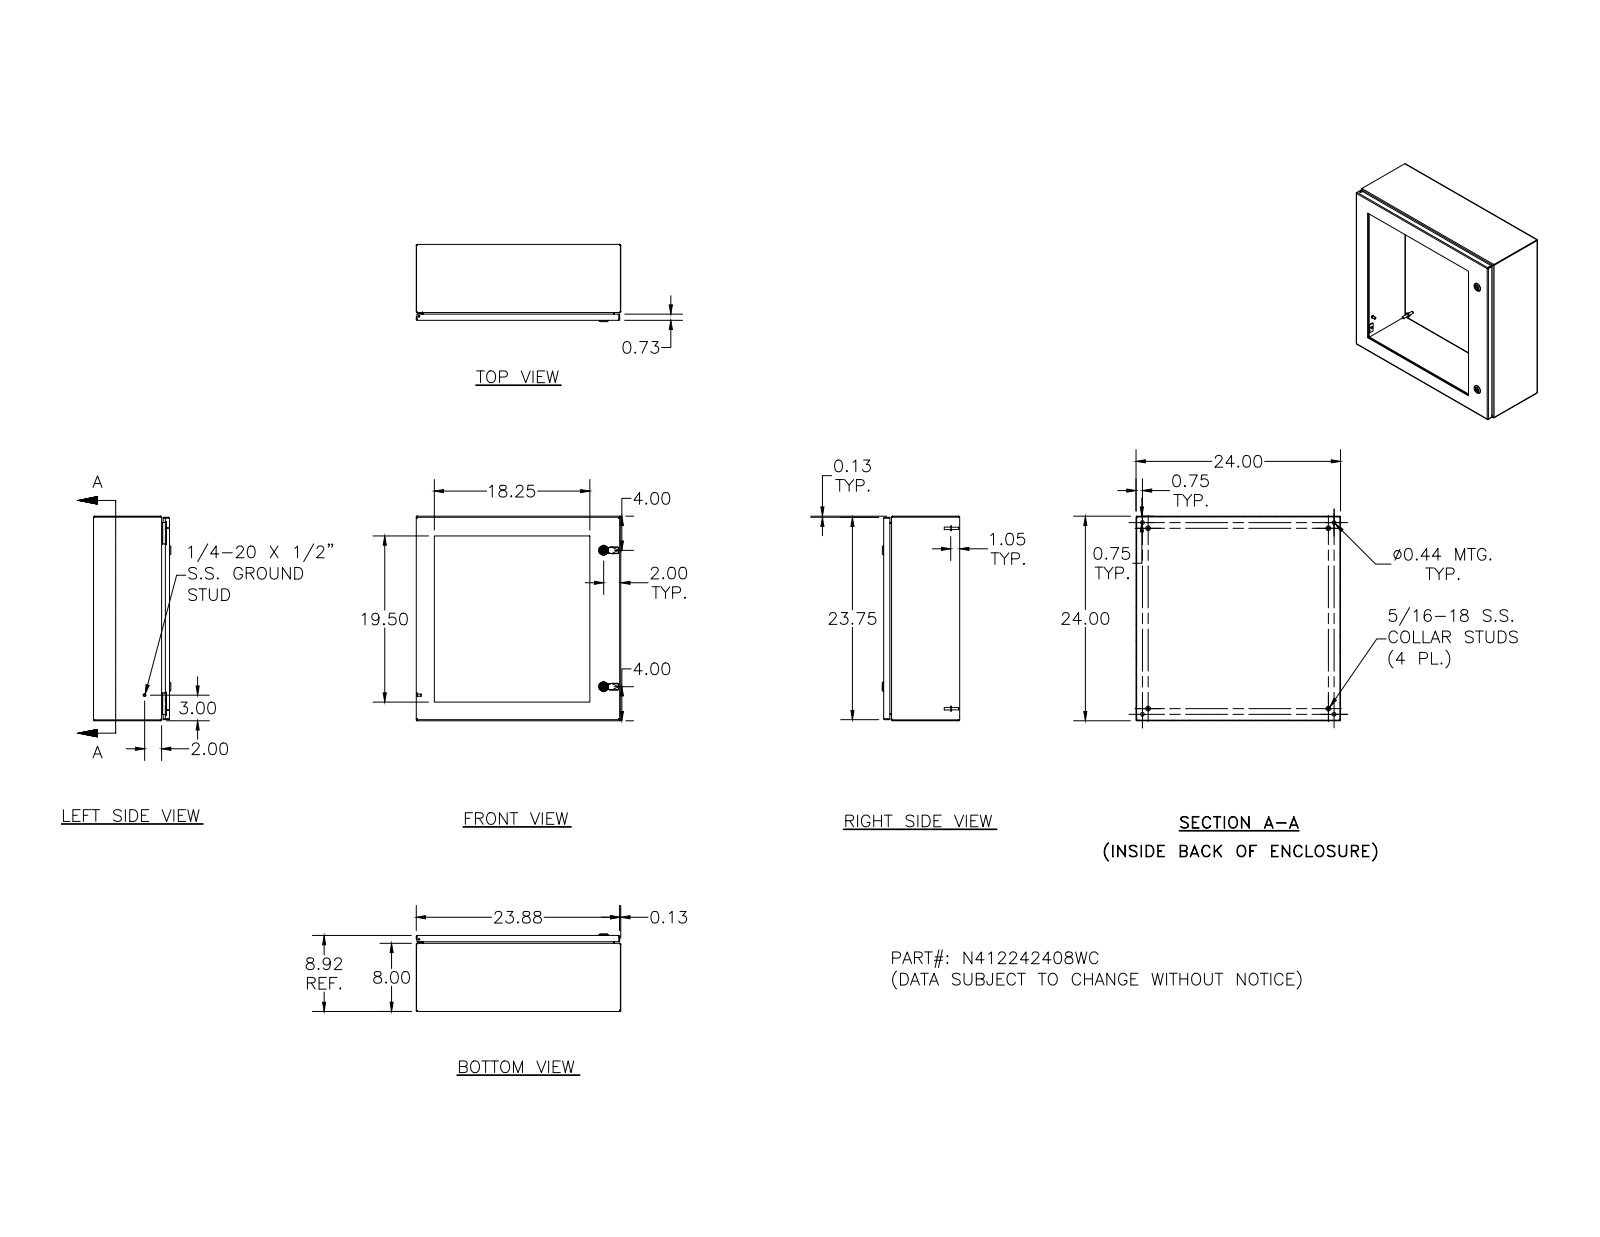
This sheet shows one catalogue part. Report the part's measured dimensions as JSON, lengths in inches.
{"part_name": "N412242408WC", "step_written_by": "SolidWorks 2018 (AUTOMOTIVE_DESIGN)", "units": "inches", "bodies": {"solids": 84, "faces": 2510, "planar": 971, "cylindrical": 762, "other": 777}, "overall_size": [24, 24, 9.075], "volume_in3": 236, "surface_area_in2": 4559, "round_holes": [[0.156, 22], [0.281, 20], [0.188, 5], [0.093, 4], [0.152, 4], [0.167, 4], [0.172, 4], [0.437, 4], [0.197, 2], [0.315, 2], [0.394, 2], [0.402, 2]], "round_bosses_or_shafts": [[0.337, 20], [0.19, 20], [0.25, 10], [0.563, 4], [0.36, 4], [0.32, 4], [0.3, 4], [0.275, 4]], "partial_cylinders_radius": [[0.012, 54], [0.031, 34], [0.05, 26], [0.105, 24], [0.02, 23], [0.016, 18], [0.125, 16], [0.032, 8]], "face_to_face_distances": [0.074, 8.843, 23.926, 8.769, 0.25, 8.593, 8.519, 24, 23.852, 8.917], "hole_center_spacings": [4, 8, 21.132, 12, 20, 22.239, 20.75, 6.221]}
